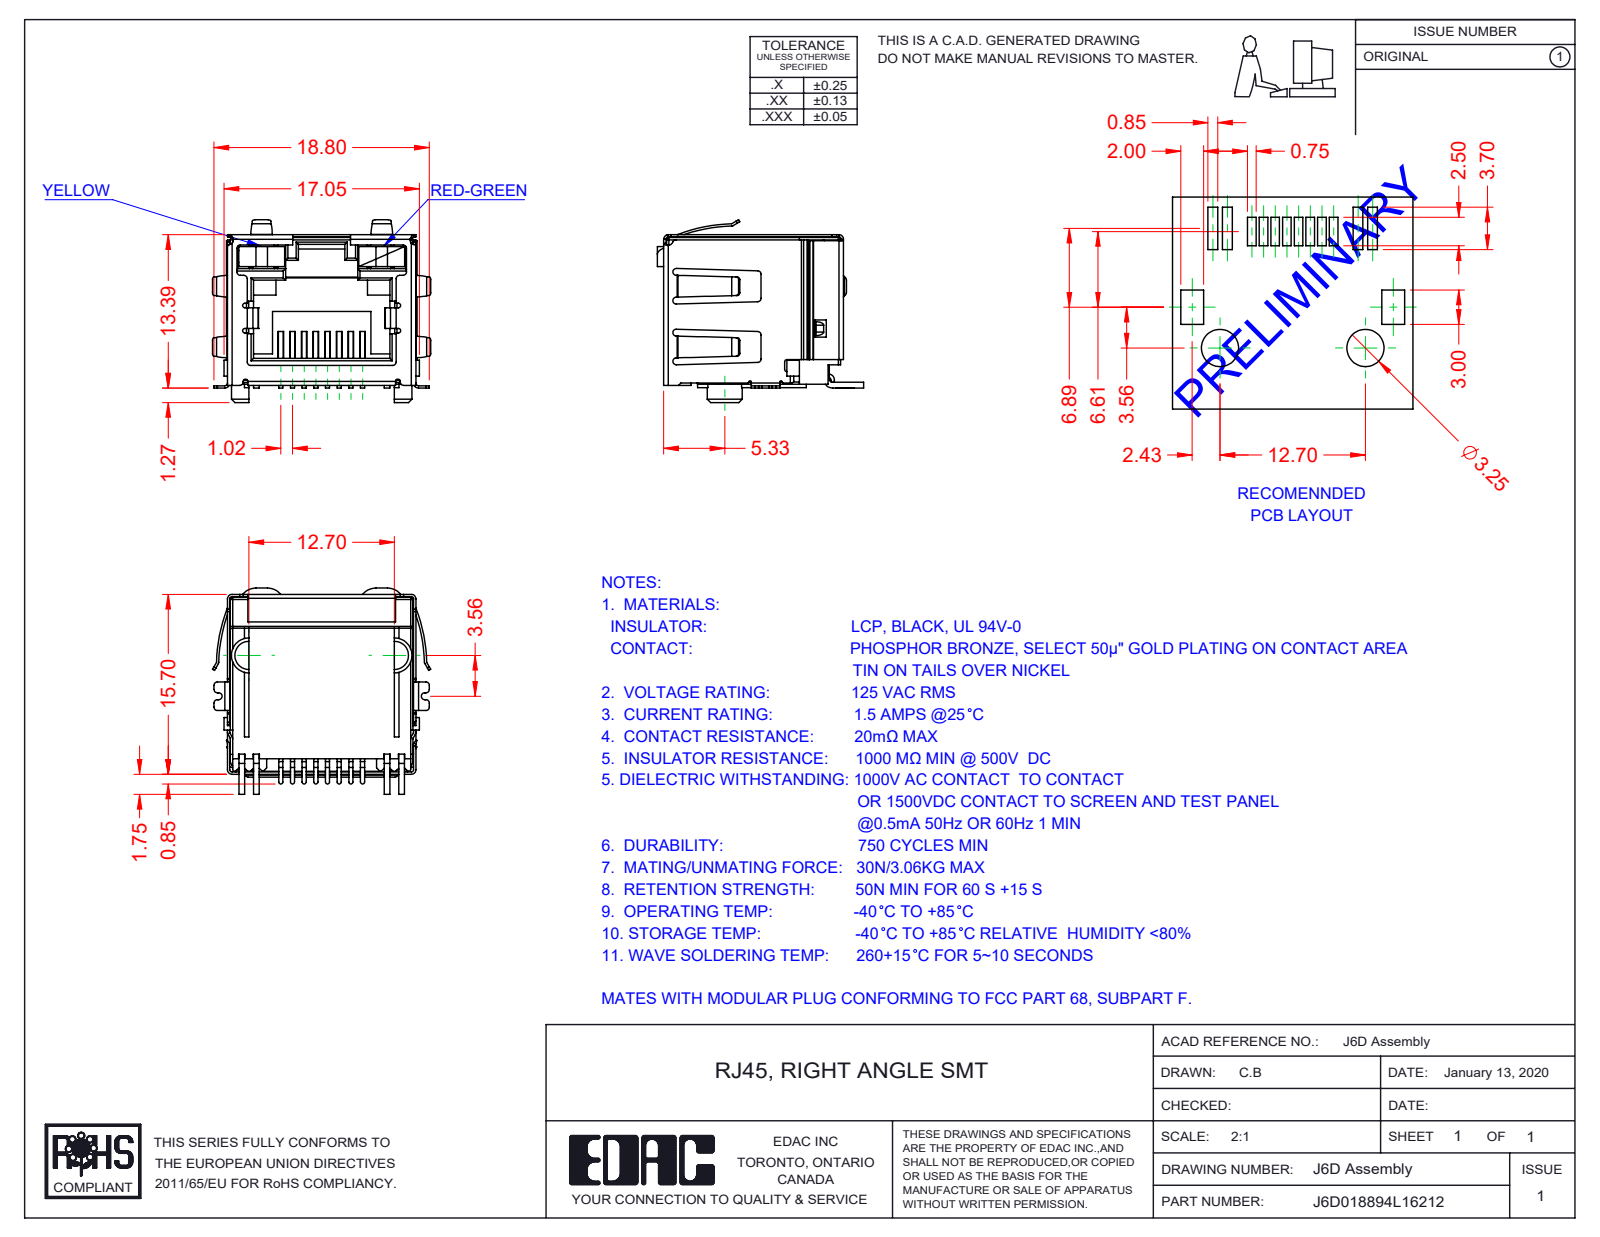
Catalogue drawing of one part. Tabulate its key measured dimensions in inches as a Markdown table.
| quantity | value |
| --- | --- |
| part name | 6D Shield_LED - EMI; 6D Insulator; 6D Contacts; 6D LED RH_6-Red-Green (+2 more) |
| STEP written by | SolidWorks 2016 (CONFIG_CONTROL_DESIGN) |
| units | inches |
| bodies | 12 solids, 1031 faces (702 planar, 284 cylindrical, 45 other) |
| overall size | 0.75 × 0.709 × 0.628 |
| volume | 0.109 in³ |
| surface area | 7.434 in² |
| partial cylindrical surfaces (radius × count) | 0.012 × 55, 0.008 × 40, 0.016 × 19, 0.01 × 16, 0.004 × 12, 0.006 × 8, 0.007 × 8, 0.02 × 6 |
| main face-to-face distances | 0.63, 0.638, 0.64, 0.089, 0.039, 0.628, 0.504, 0.018, 0.514, 0.417 |
